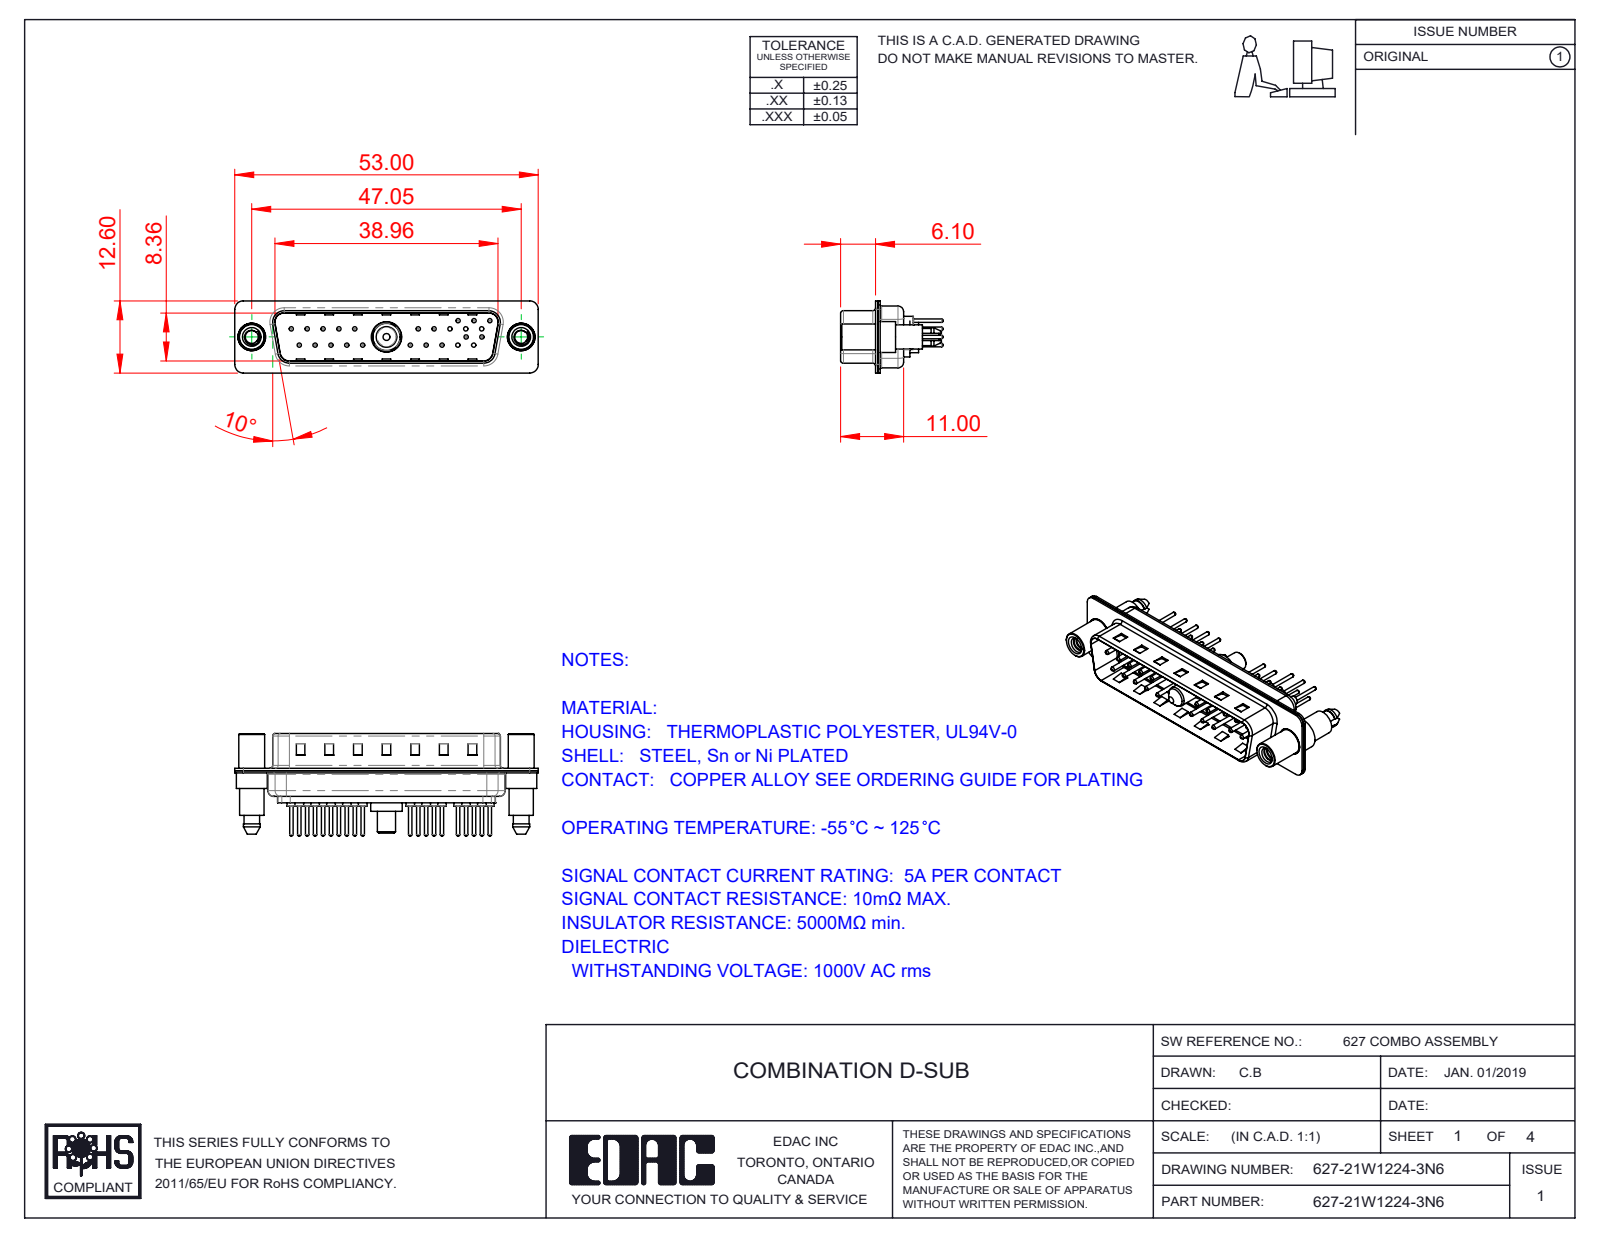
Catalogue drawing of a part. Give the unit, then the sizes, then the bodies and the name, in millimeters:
Units: millimetres
Overall size (bounding box): 53 × 17.9 × 12.6
Round holes (diameter × count): ⌀0.75 ×20, ⌀1.6 ×20, ⌀2 ×20, ⌀2.26 ×2, ⌀4 ×2, ⌀4.8 ×2, ⌀4.85 ×1, ⌀5.3 ×1
Round bosses / shafts (diameter × count): ⌀1.5 ×20, ⌀0.6 ×20, ⌀2 ×5, ⌀0.75 ×5, ⌀5.4 ×2, ⌀4.9 ×2, ⌀4.5 ×2, ⌀4.25 ×2
Partial cylindrical surfaces — rounded edges, fillets, slot ends (radius × count): R1.5 ×18, R2 ×12, R1.6 ×10, R0.5 ×8, R0.25 ×4, R0.6 ×4, R0.65 ×4, R0.9 ×4
Main face-to-face distances: 0.4, 0.82, 9.58, 8.76, 1.5, 5.2, 5.6, 6, 0.8, 1.22
Hole centre spacings: 3.16, 2.77, 5.54, 8.31, 5.04, 19.39, 20.97, 22.16
Volume: 3 133 mm³ · Surface area: 7 300 mm²
Bodies: 27 solids, 1208 faces (339 planar, 464 cylindrical, 405 other)
Part name (STEP PRODUCT): 627Combo Shell Rear_25 Contacts; 627Combo Contact Row 2_24; Power Pin_30A S; 627Combo Shell Front_25 Contacts (+4 more)
STEP written by: SolidWorks 2016 (CONFIG_CONTROL_DESIGN)
